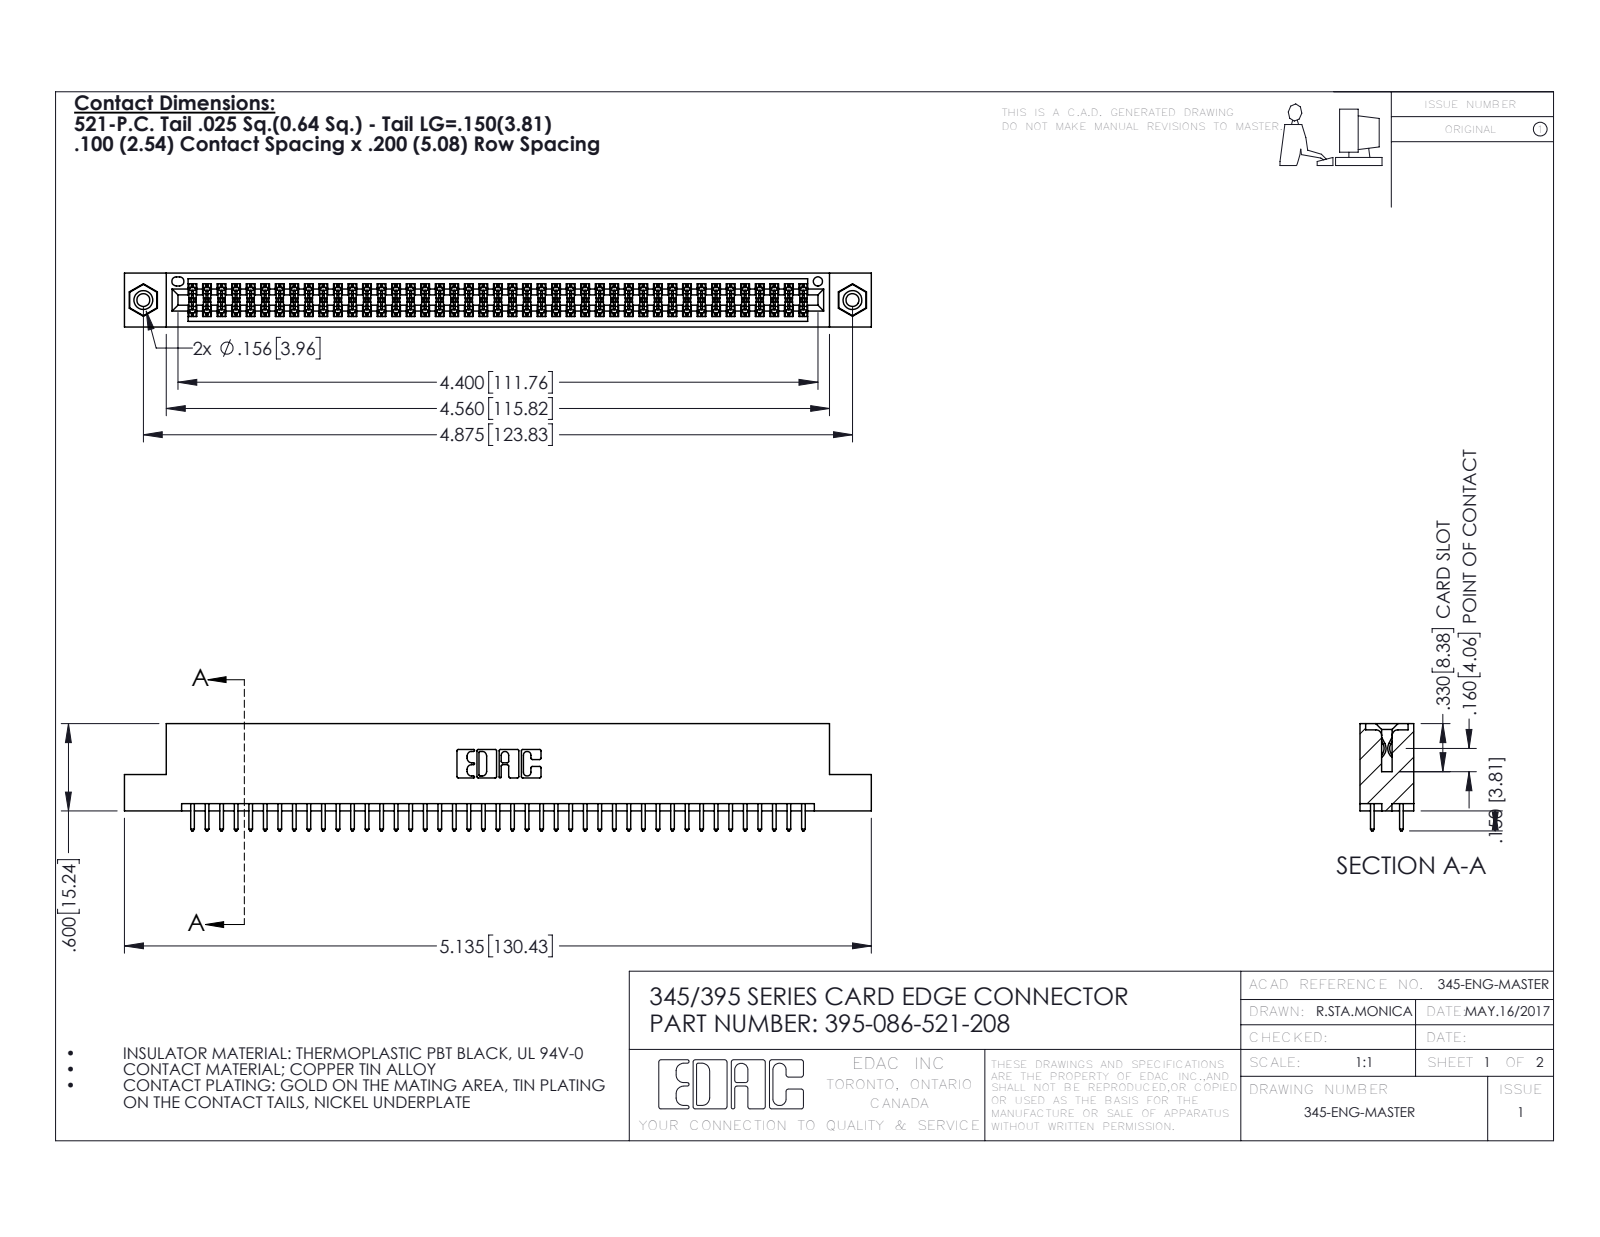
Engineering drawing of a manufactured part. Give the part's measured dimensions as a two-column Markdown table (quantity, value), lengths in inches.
| quantity | value |
| --- | --- |
| part name | 395-086-521-208; 345 Part_Flush Mounting Lugs - 0.156 Dia-TI; 345-292-001_345-293-121; 345-250-001_345-250-003-102 |
| STEP written by | SolidWorks 2016 (CONFIG_CONTROL_DESIGN) |
| units | inches |
| bodies | 89 solids, 4486 faces (2950 planar, 1520 cylindrical, 16 other) |
| overall size | 5.135 × 0.737 × 0.37 |
| volume | 0.771 in³ |
| surface area | 28.65 in² |
| round holes (diameter × count) | 0.089 × 2, 0.125 × 2, 0.156 × 2, 0.064 × 1 |
| round bosses / shafts (diameter × count) | 0.155 × 2 |
| partial cylindrical surfaces (radius × count) | 0.006 × 129, 0.01 × 86, 0.01 × 22, 0.007 × 6, 0.031 × 6, 0.026 × 3, 0.014 × 2, 0.019 × 2 |
| main face-to-face distances | 0.072, 0.298, 0.2, 0.37, 0.098, 0.272, 0.025, 0.225, 0.175, 0.149 |
| hole center spacings | 0.27, 4.639, 4.875 |
